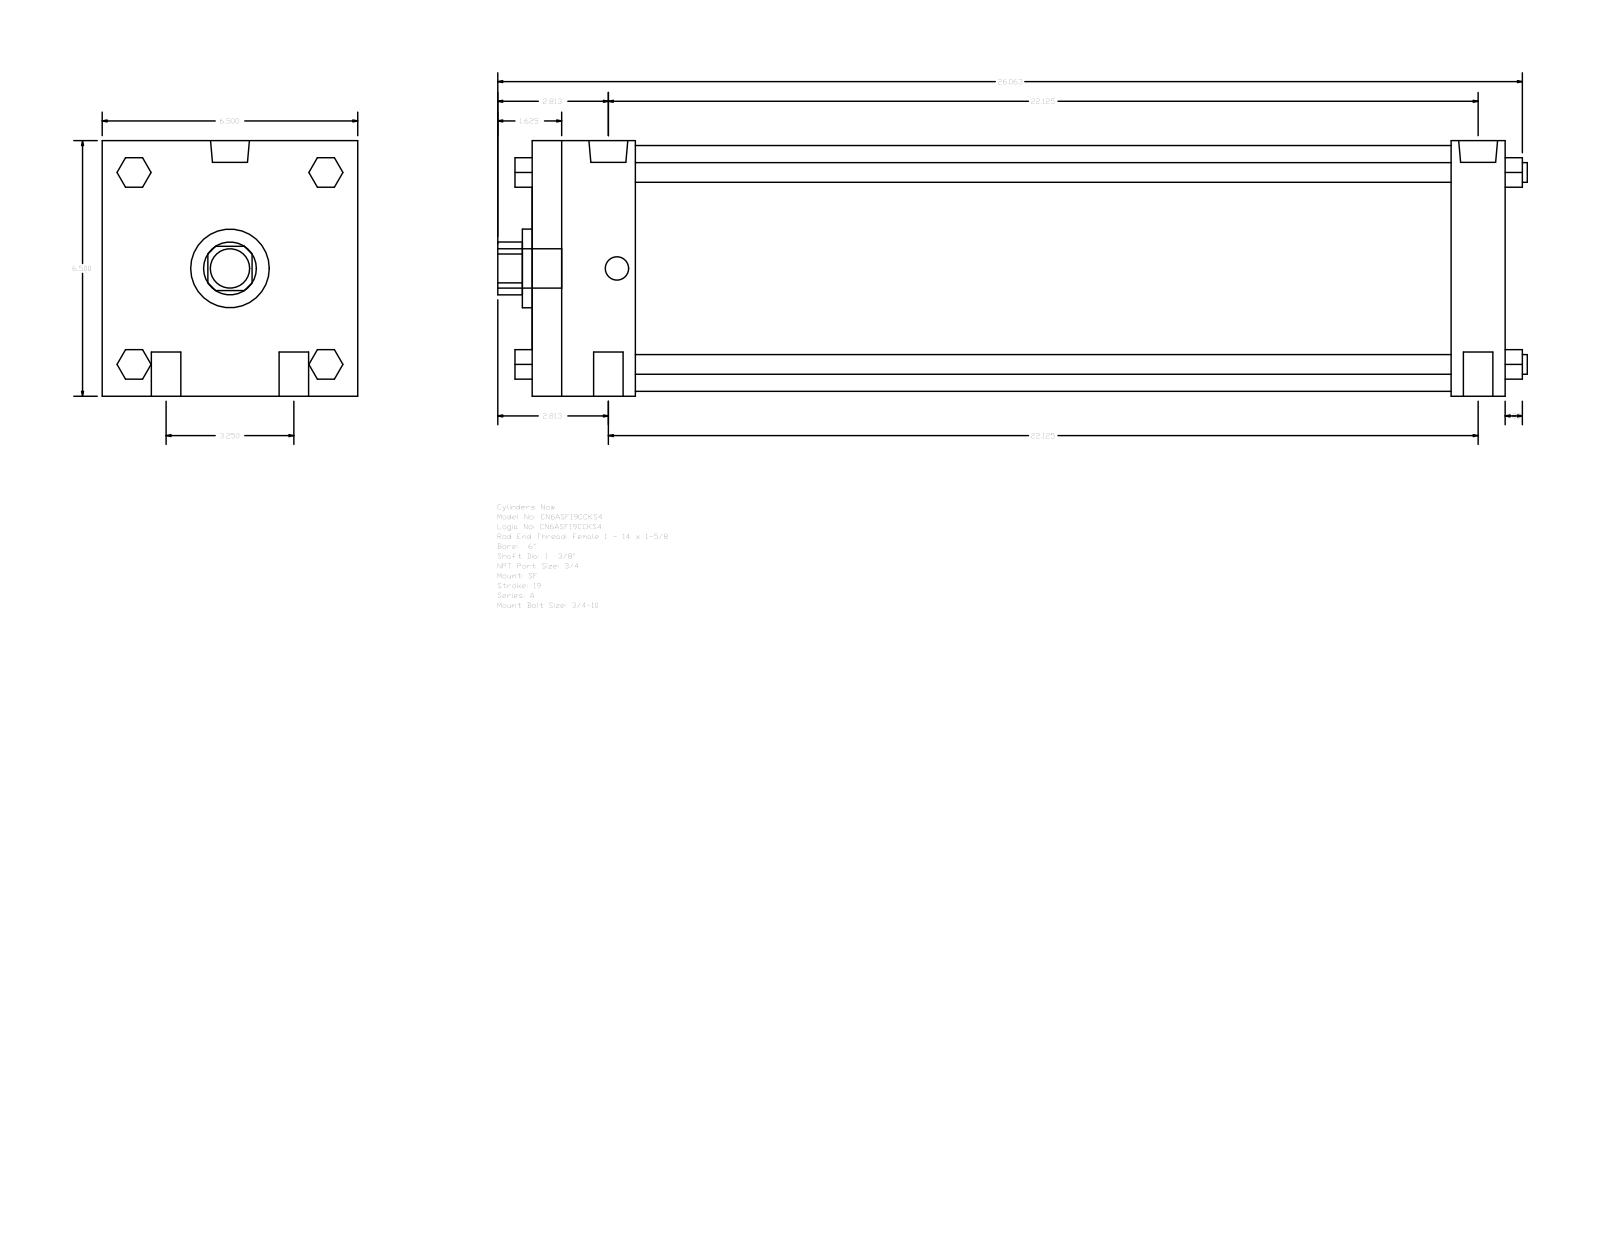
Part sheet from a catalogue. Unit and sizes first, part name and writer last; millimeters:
Units: millimetres
Overall size (bounding box): 665.16 × 165.1 × 165.1
Round holes (diameter × count): ⌀34.92 ×1, ⌀50.8 ×1, ⌀158.75 ×1
Round bosses / shafts (diameter × count): ⌀19.05 ×4, ⌀12.7 ×4, ⌀25.12 ×2, ⌀15.08 ×2, ⌀25.4 ×1
Partial cylindrical surfaces — rounded edges, fillets, slot ends (radius × count): R17.06 ×1
Main face-to-face distances: 165.1, 628.65, 593.72, 34.93, 66.67, 527.05, 561.98, 19.05, 61.97, 107.34
Bodies: 0 solids, 124 faces (94 planar, 30 cylindrical, 0 other)
Part name (STEP PRODUCT): A_SF__0600_1.375
STEP written by: GSSL Pune (CONFIG_CONTROL_DESIGN)
